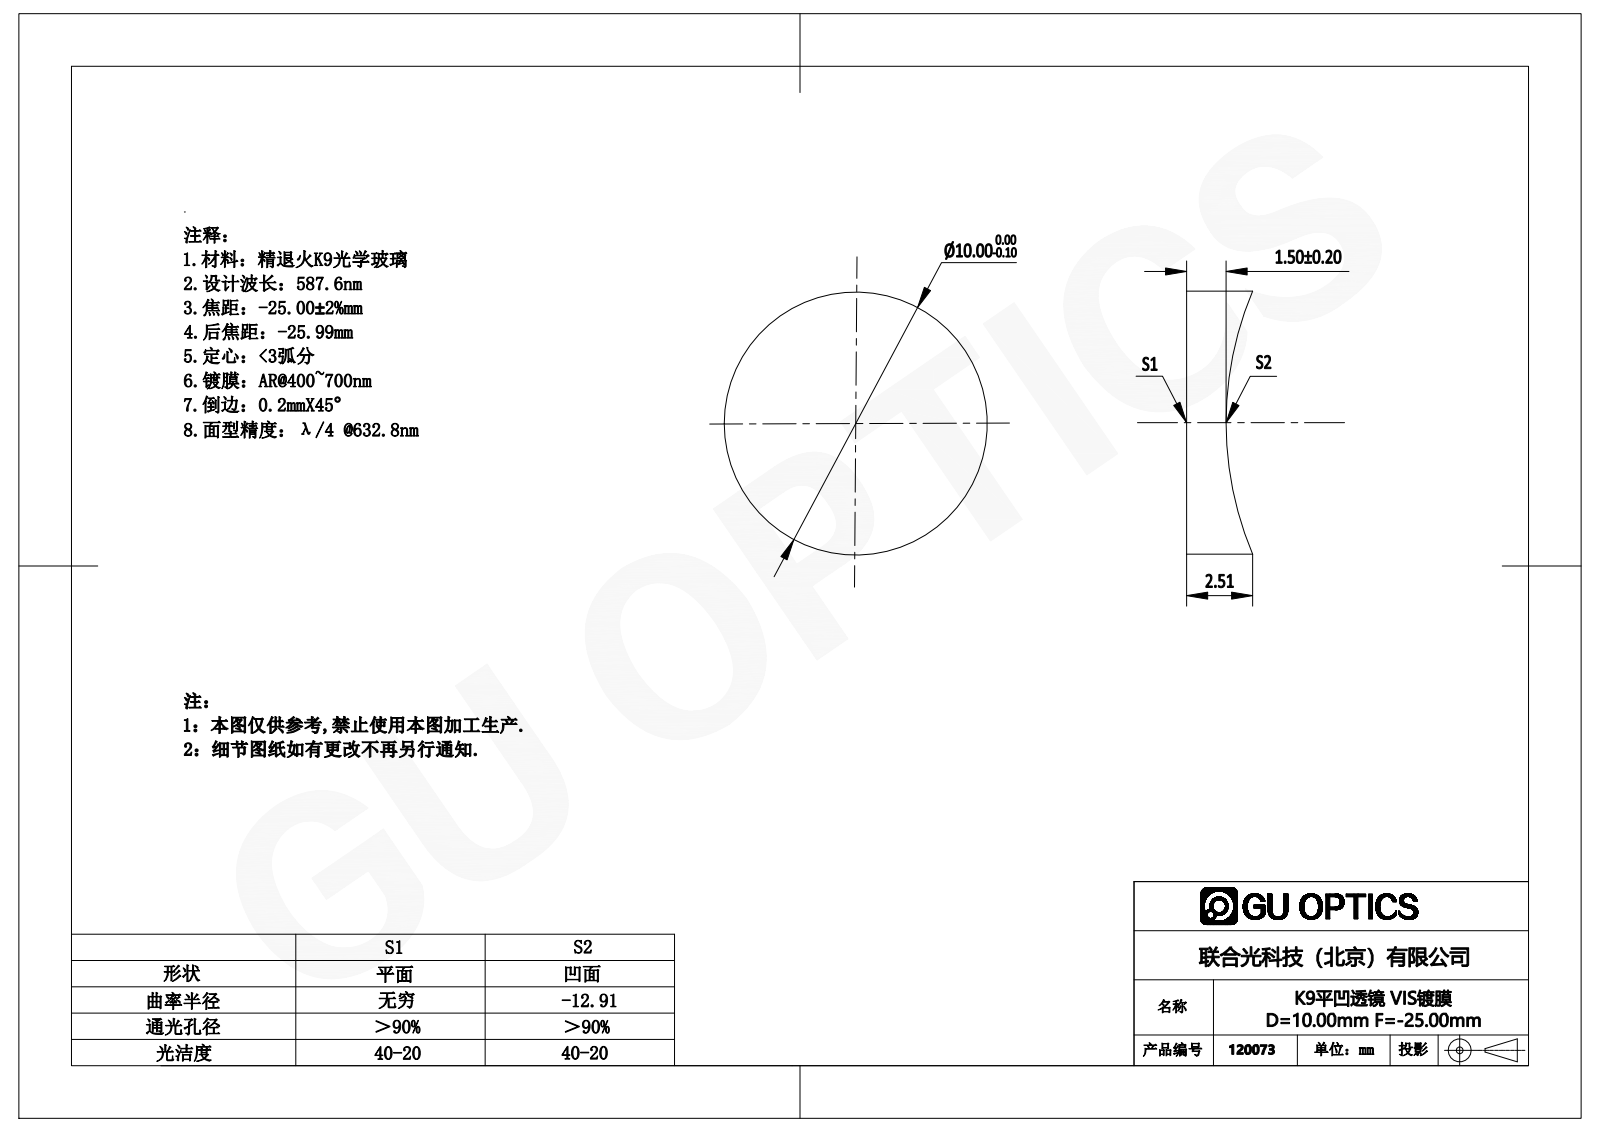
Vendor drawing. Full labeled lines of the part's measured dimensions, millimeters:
Part name (STEP PRODUCT): 120013
STEP written by: SolidWorks 2016 (AUTOMOTIVE_DESIGN)
Units: millimetres
Bodies: 1 solid, 5 faces (1 planar, 2 cylindrical, 2 other)
Overall size (bounding box): 10 × 10 × 2.51
Volume: 157 mm³ · Surface area: 239 mm²
Round bosses / shafts (diameter × count): ⌀10 ×1
